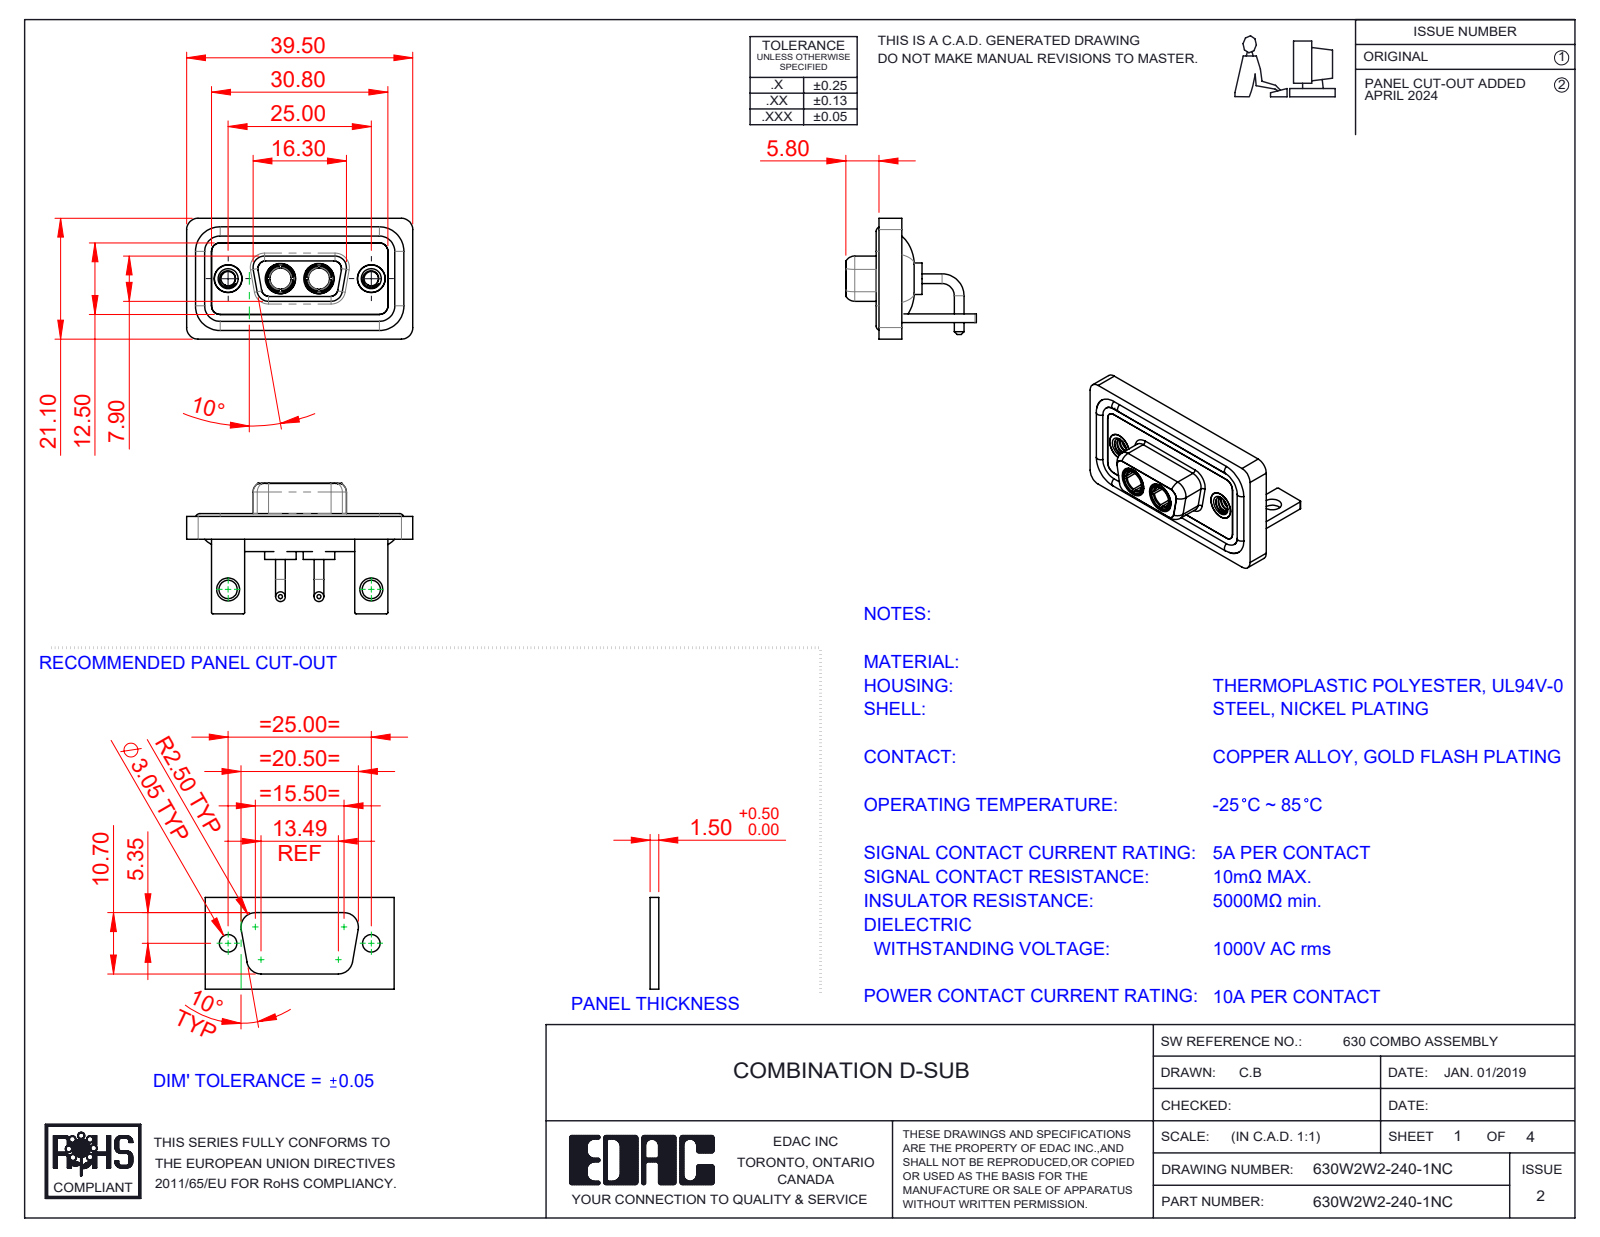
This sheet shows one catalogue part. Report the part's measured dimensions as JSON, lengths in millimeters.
{"part_name": "630Combo Waterproof Housing_09 Contacts; 630Combo Shell Rear_09 Contacts; 630W2W2-240-1NC; 630Combo Stabilizer Bracket_50 Contacts (+4 more)", "step_written_by": "SolidWorks 2023 (CONFIG_CONTROL_DESIGN)", "units": "millimeters", "bodies": {"solids": 13, "faces": 584, "planar": 183, "cylindrical": 260, "other": 141}, "overall_size": [39.5, 22.8, 21.1], "volume_mm3": 5060, "surface_area_mm2": 8423, "round_holes": [[4.85, 4], [2.5, 2], [3.2, 2], [3.7, 2], [4, 2], [4.05, 2], [5, 2], [5.3, 2]], "round_bosses_or_shafts": [[1.7, 4], [1.6, 4], [5.5, 2], [5.2, 2], [4.96, 2], [4.95, 2], [4.8, 2], [4.75, 2]], "partial_cylinders_radius": [[2, 19], [1.5, 18], [0.25, 16], [1.35, 8], [1.6, 8], [0.5, 5], [0.6, 4], [0.65, 4]], "face_to_face_distances": [0.4, 2.9, 1.5, 1.8, 1.1, 3.7, 0.8, 2.5, 1.6, 3.1], "hole_center_spacings": [9.14, 15.86, 25, 6.72]}
